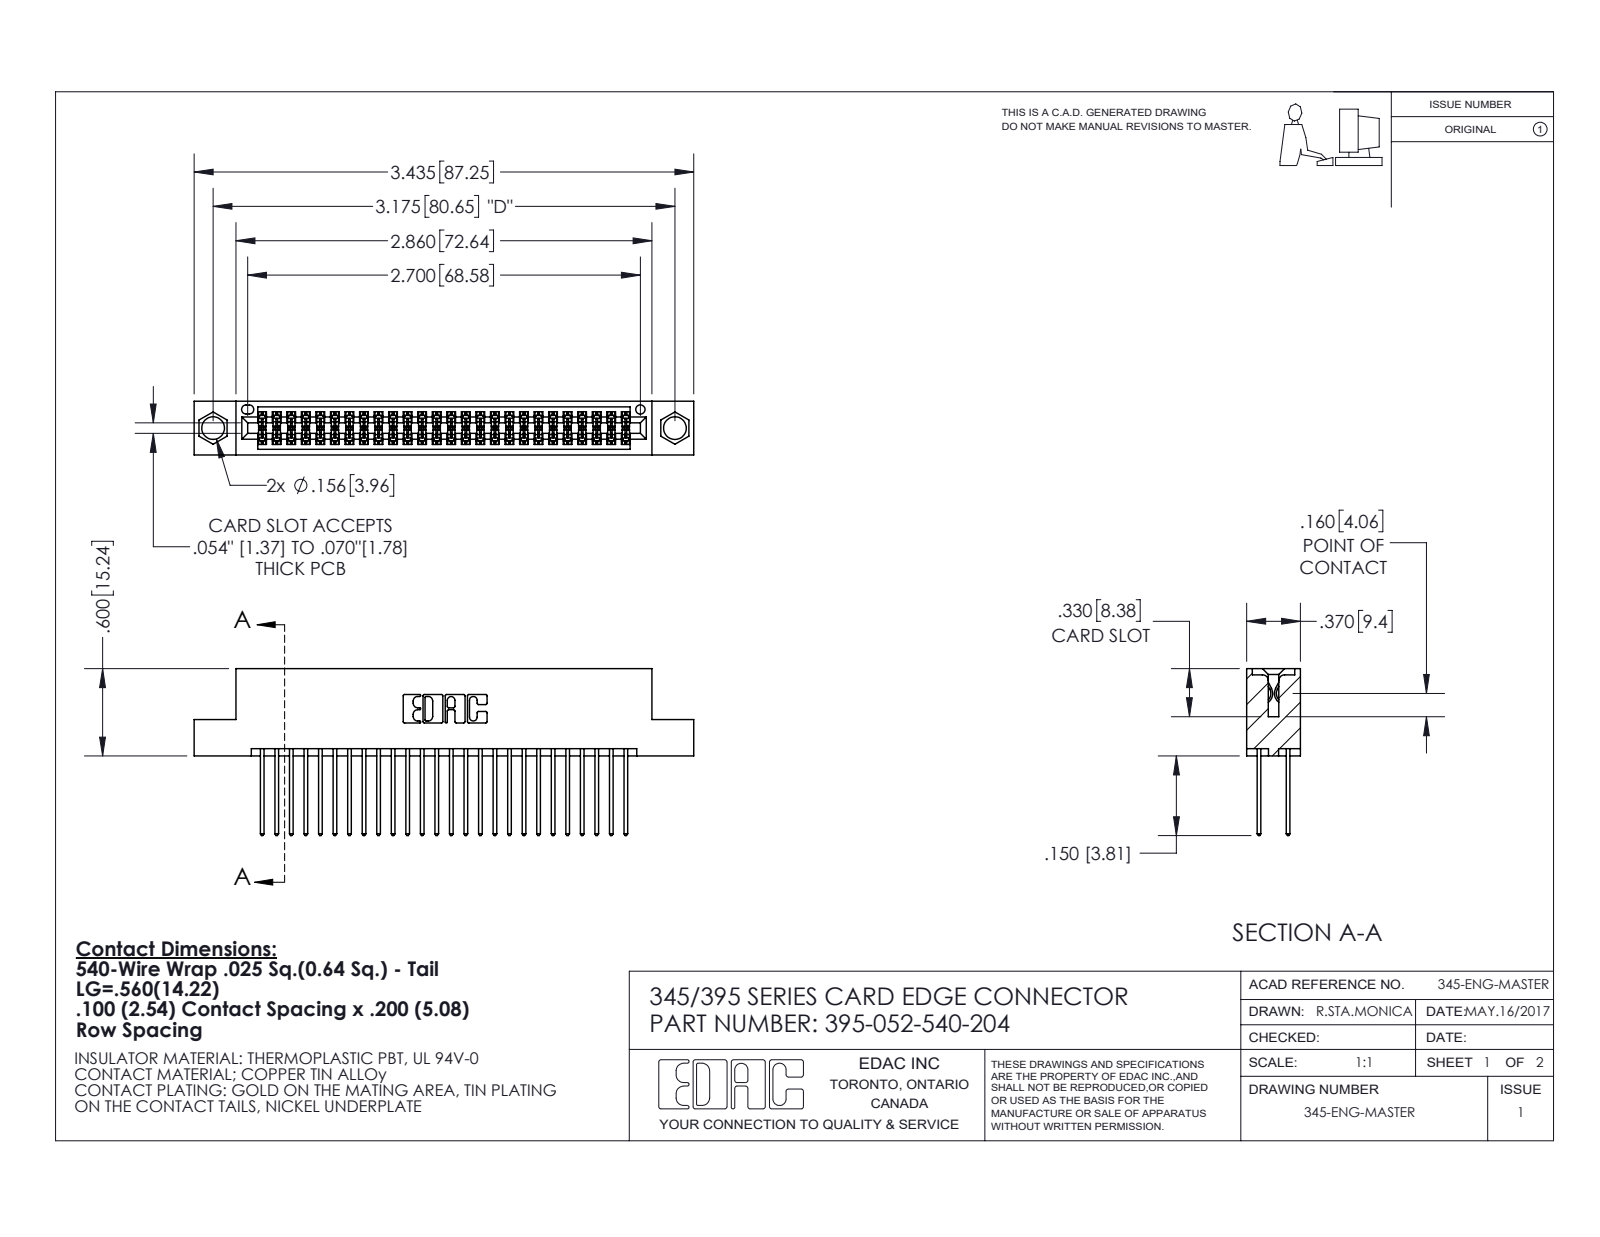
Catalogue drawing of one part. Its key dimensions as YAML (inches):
part_name: "345-292-001_345-293-140; 395-052-540-204; 345 Part_Flush Mounting Lugs - 0.156 Dia-TI"
step_written_by: "SolidWorks 2020 (CONFIG_CONTROL_DESIGN)"
units: inches
bodies: {solids: 53, faces: 2740, planar: 1810, cylindrical: 930, other: 0}
overall_size: [3.435, 1.147, 0.37]
volume: 0.514
surface_area: 19.99
round_holes:
  - {diameter: 0.156, count: 2}
  - {diameter: 0.064, count: 1}
partial_cylinders:
  - {radius: 0.006, count: 104}
  - {radius: 0.01, count: 52}
  - {radius: 0.01, count: 22}
  - {radius: 0.007, count: 6}
  - {radius: 0.031, count: 6}
  - {radius: 0.026, count: 3}
  - {radius: 0.014, count: 2}
  - {radius: 0.019, count: 2}
face_to_face_distances: [0.072, 0.298, 0.2, 0.098, 0.272, 0.025, 0.37, 0.225, 0.175, 0.149]
hole_center_spacings: [0.27, 2.94, 3.175]
